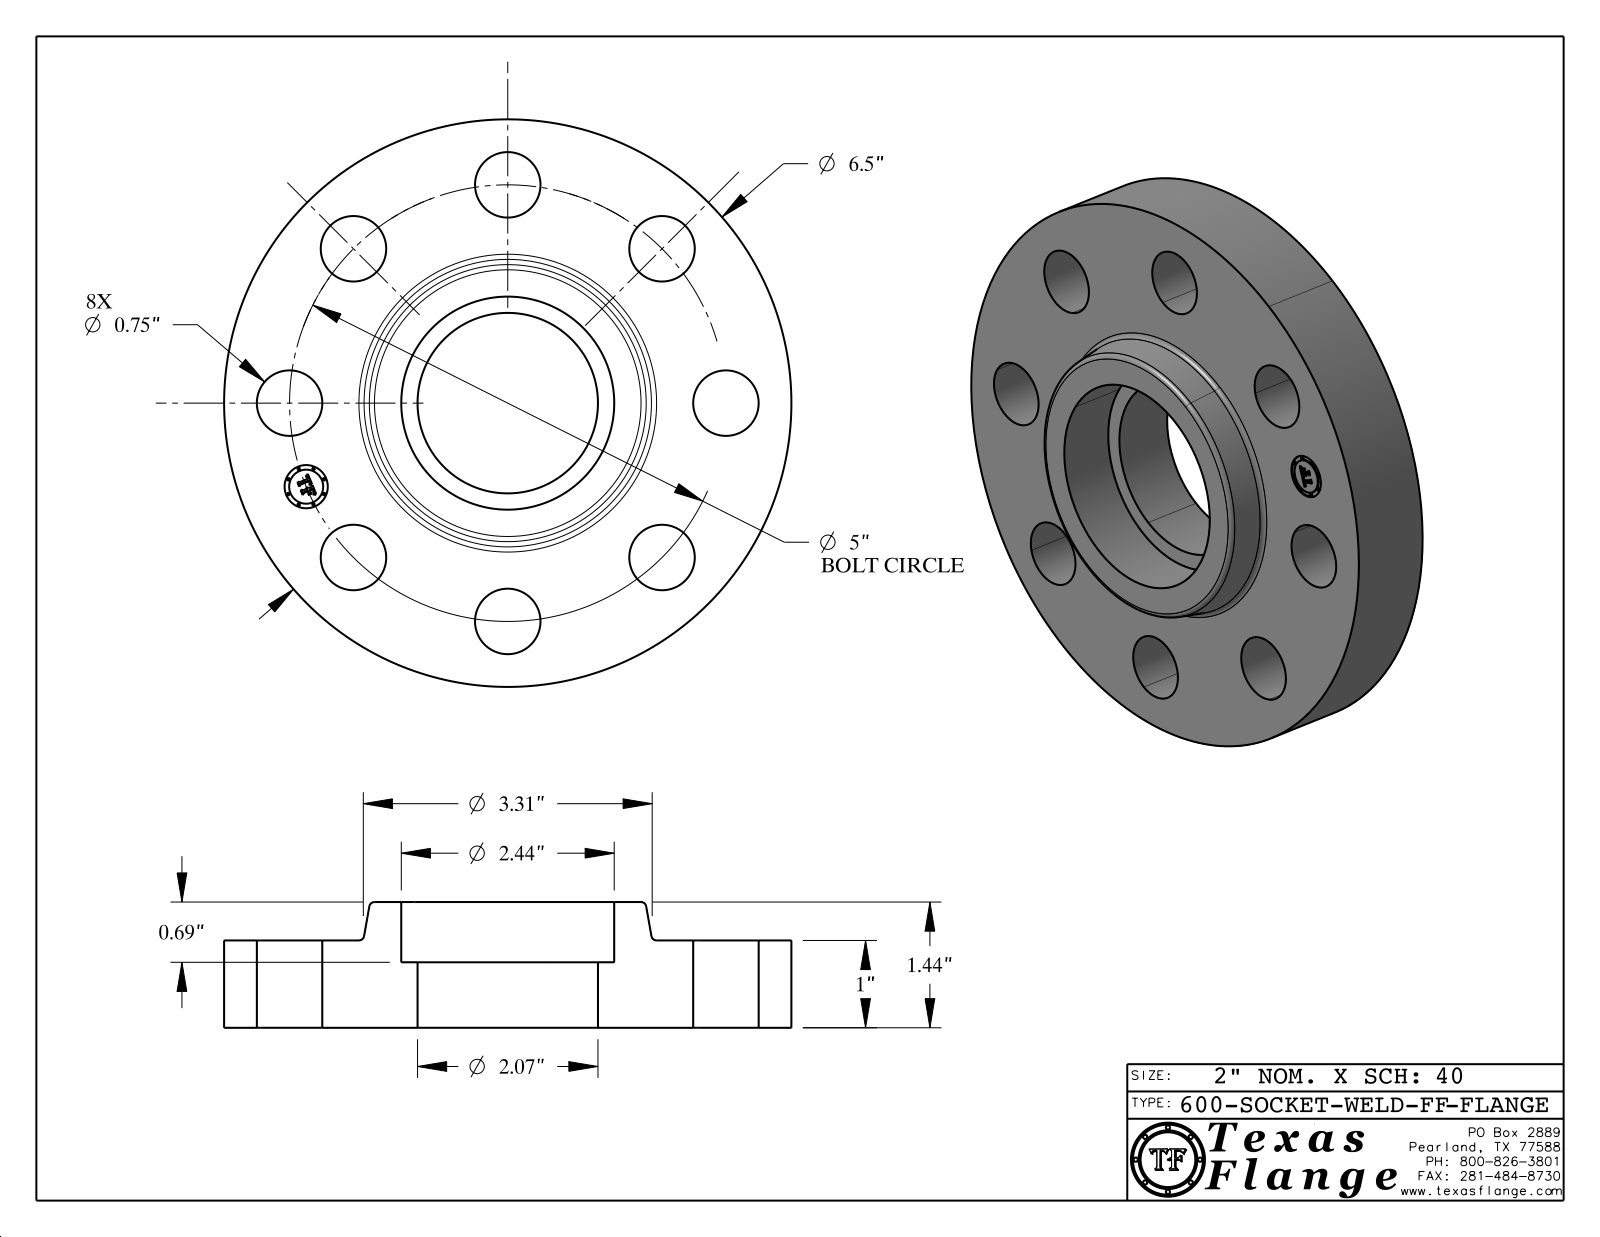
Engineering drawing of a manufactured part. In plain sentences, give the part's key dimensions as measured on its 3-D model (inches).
The part is named "600-SOCKET-WELD-FF". Its 3-D file was written by "CATIA V5 STEP AP214 (AUTOMOTIVE_DESIGN)". It is 1 solid with 417 faces: 369 planar, 42 cylindrical and 6 other. Overall it measures 6.5 by 6.5 by 1.44 inches. Its volume is 27.52 cubic inches and its surface area 105.5 square inches. Round holes: 8 of diameter 0.75, 1 of diameter 0.495, 1 of diameter 2.067, 1 of diameter 2.44. Round bosses or shafts: 8 of diameter 0.03, 1 of diameter 6.5, 1 of diameter 0.39. The main face-to-face distances are 1, 1.44, 0.44, 0.75, 0.25, 0.69, 0.985, 0.235, 0.015, 0.455. The hole center spacings are 2.5, 1.913, 3.535, 4.619, 5, 0.976, 2.778, 4.157.
